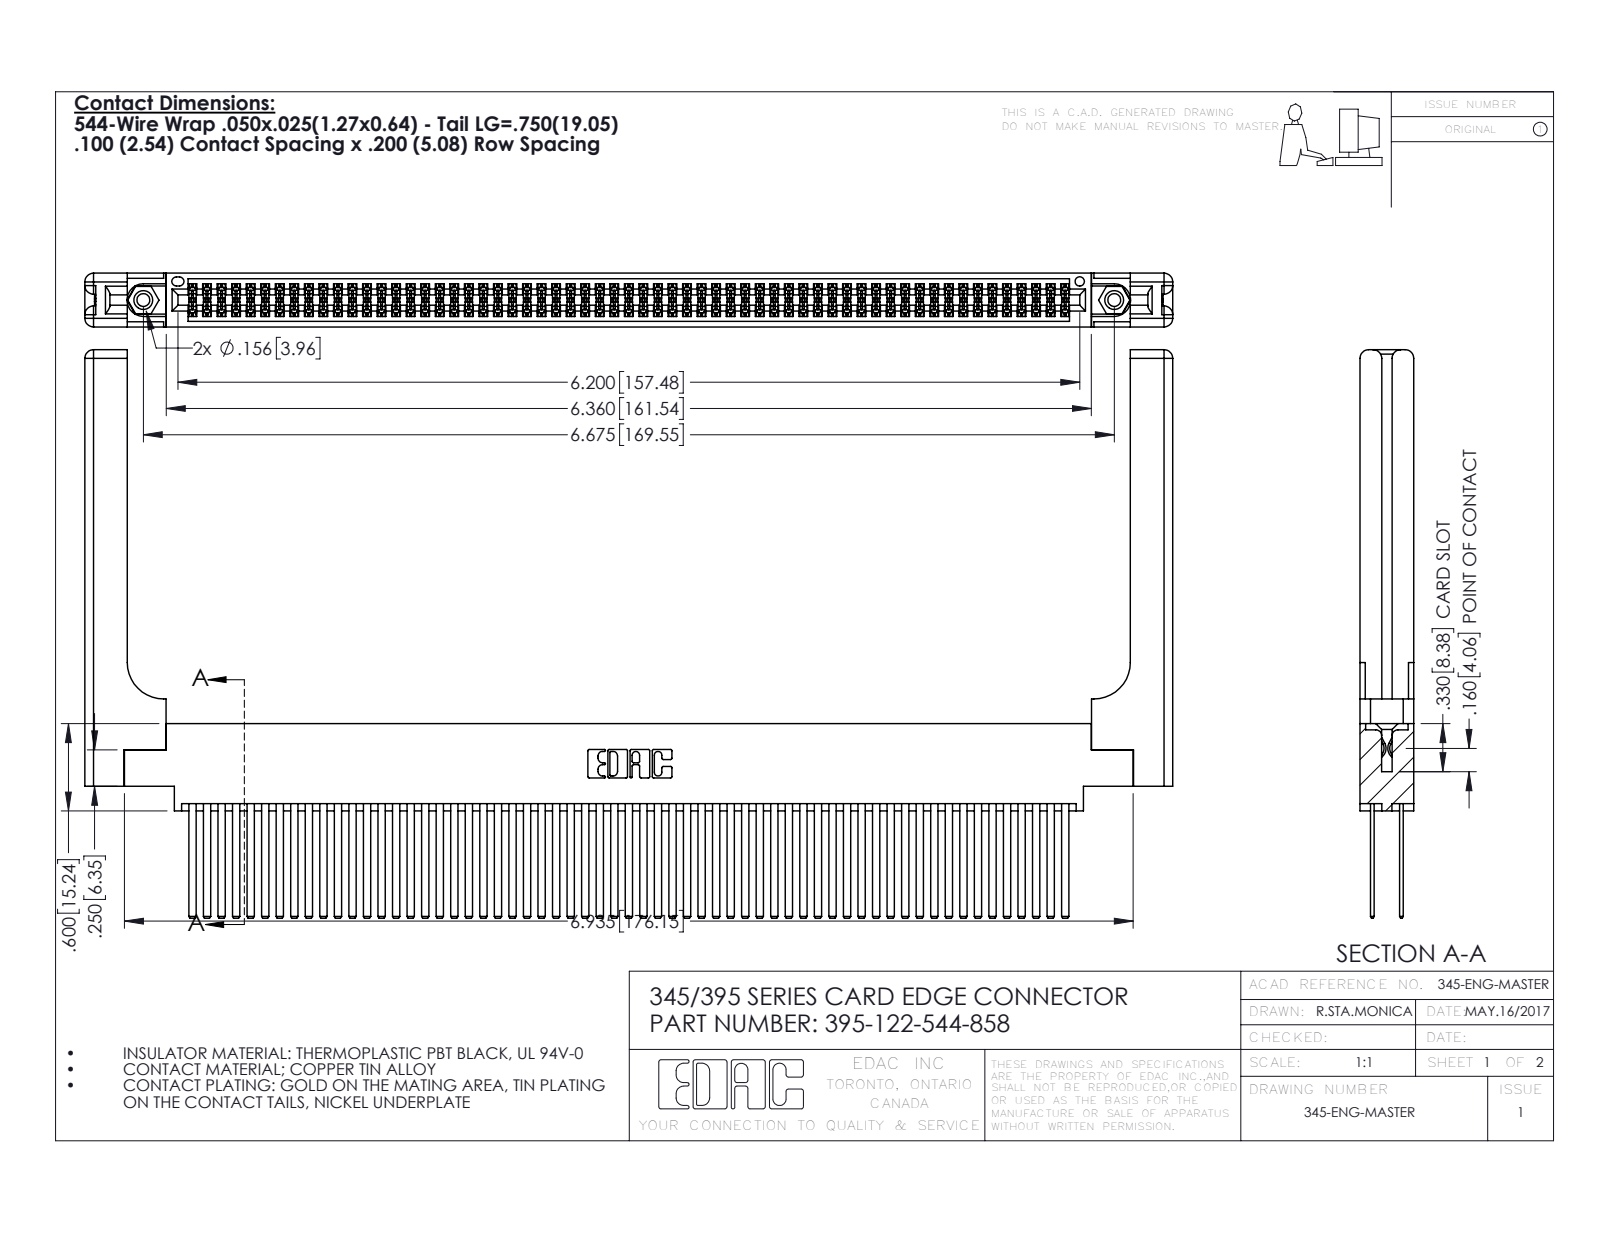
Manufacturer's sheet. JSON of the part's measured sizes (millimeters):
{"part_name": "345 Part_0.170 Offset - 0.156 Dia-TH; 395-122-544-858; 345-220-058_345-220-058; 345-250-001_345-250-001-102 (+1 more)", "step_written_by": "SolidWorks 2016 (CONFIG_CONTROL_DESIGN)", "units": "millimeters", "bodies": {"solids": 127, "faces": 5754, "planar": 3770, "cylindrical": 1924, "other": 60}, "overall_size": [190, 99.2, 9.4], "volume_mm3": 28690, "surface_area_mm2": 40480, "round_holes": [[2.3, 2], [3.2, 2], [4, 2], [1.6, 1]], "round_bosses_or_shafts": [[3.9, 2]], "partial_cylinders_radius": [[0.2, 183], [0.3, 22], [1.5, 16], [0.2, 6], [0.8, 6], [0.7, 3], [0.4, 2], [0.5, 2]], "face_to_face_distances": [1.8, 7.6, 2.5, 6.9, 0.6, 5.1, 9.4, 5.7, 4.4, 3.8], "hole_center_spacings": [6.9, 163.6, 169.5]}
